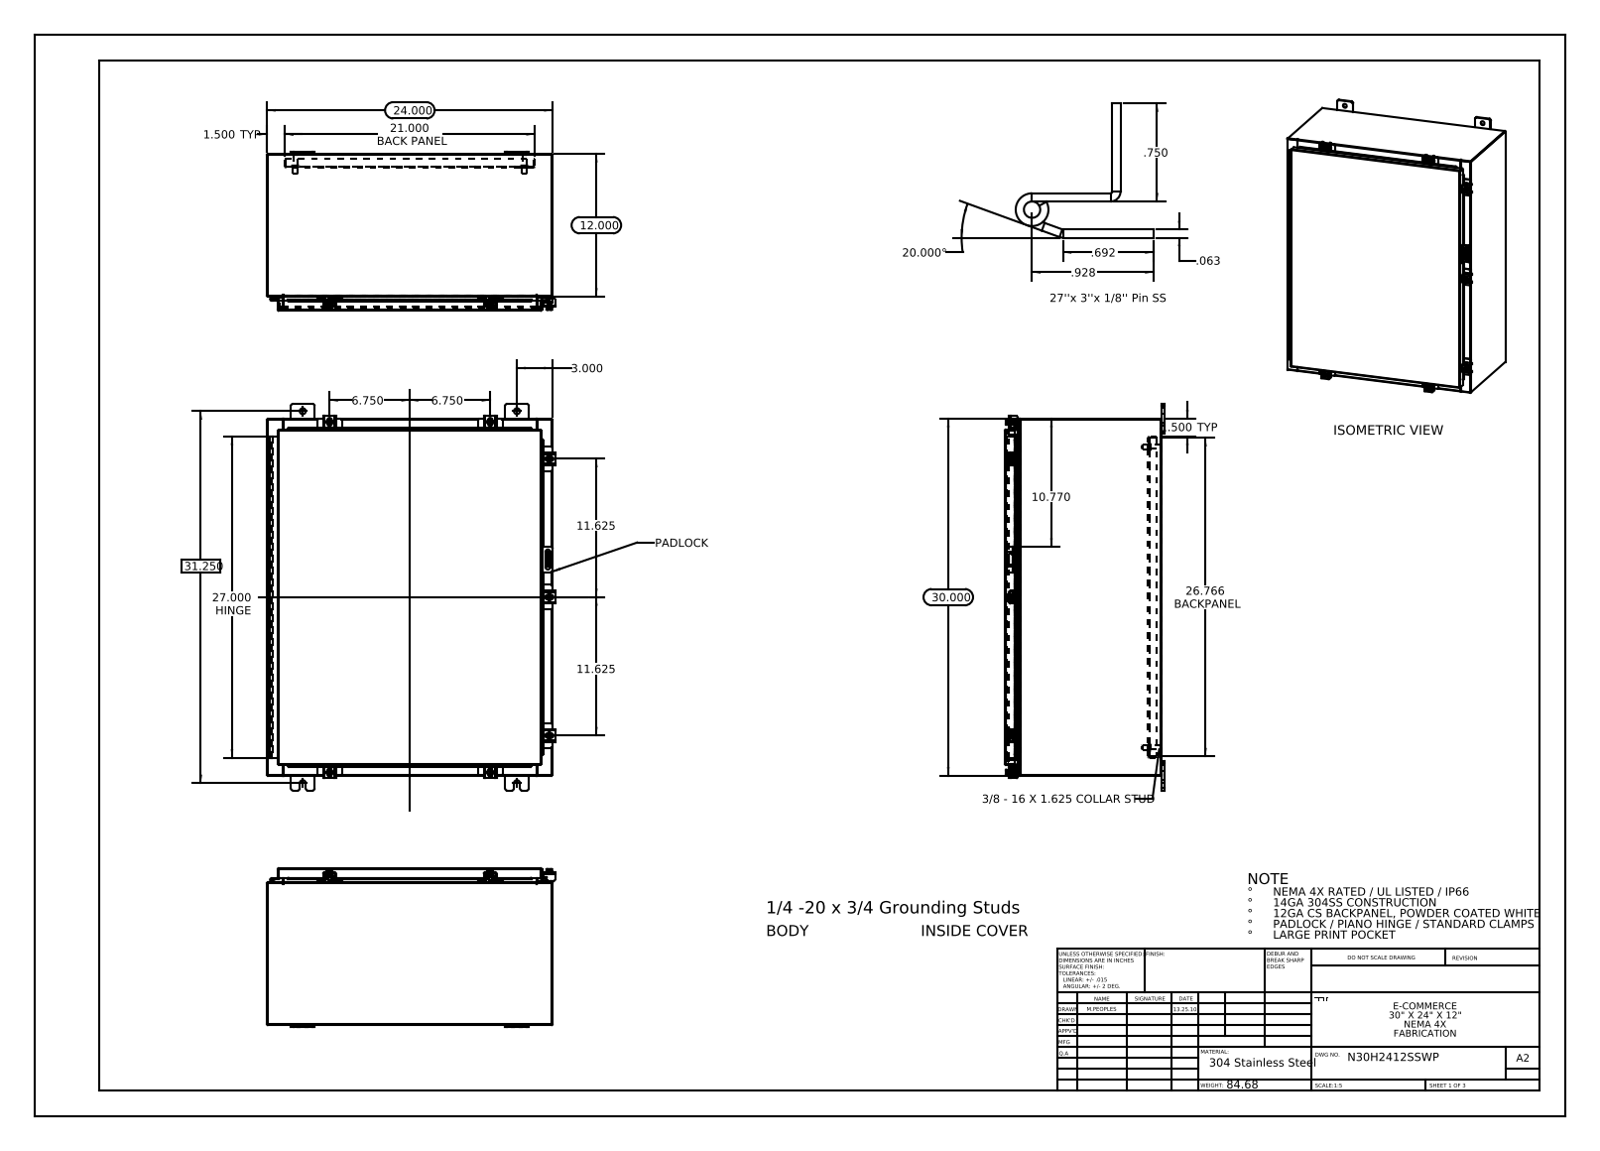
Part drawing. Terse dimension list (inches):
name: N30H2412SSWP 22104005_DEFAULT; N30H2412SSWP Clamp Bracket; N30H2412SSWP 125 Pin Hinge; N30H2412SSWP Body (+8 more)
written by: SolidWorks 2013 (CONFIG_CONTROL_DESIGN)
unit: in
bodies: 52 solids, 1990 faces (1056 planar, 830 cylindrical, 104 other)
size: 32.5 × 24.211 × 13.389
volume: 296.9 in³; area: 7 480 in²
holes: 8× ⌀0.5, 7× ⌀0.213, 7× ⌀0.26, 2× ⌀0.125, 1× ⌀0.125
bosses: 8× ⌀0.25, 7× ⌀0.5, 7× ⌀0.399, 4× ⌀0.625, 4× ⌀0.375, 4× ⌀0.33
rounds: 34× R0.06, 27× R0.013, 24× R0.19, 21× R0.088, 14× R0.12, 14× R0.141, 11× R0.05, 10× R0.08
face distances: 0.075, 13.126, 23.925, 13.201, 13.051, 0.104, 1, 29.925, 1.075, 12.051
hole spacings: 27.501, 31.878, 1.858, 2.277, 2.326, 2.423, 3.561, 3.561
